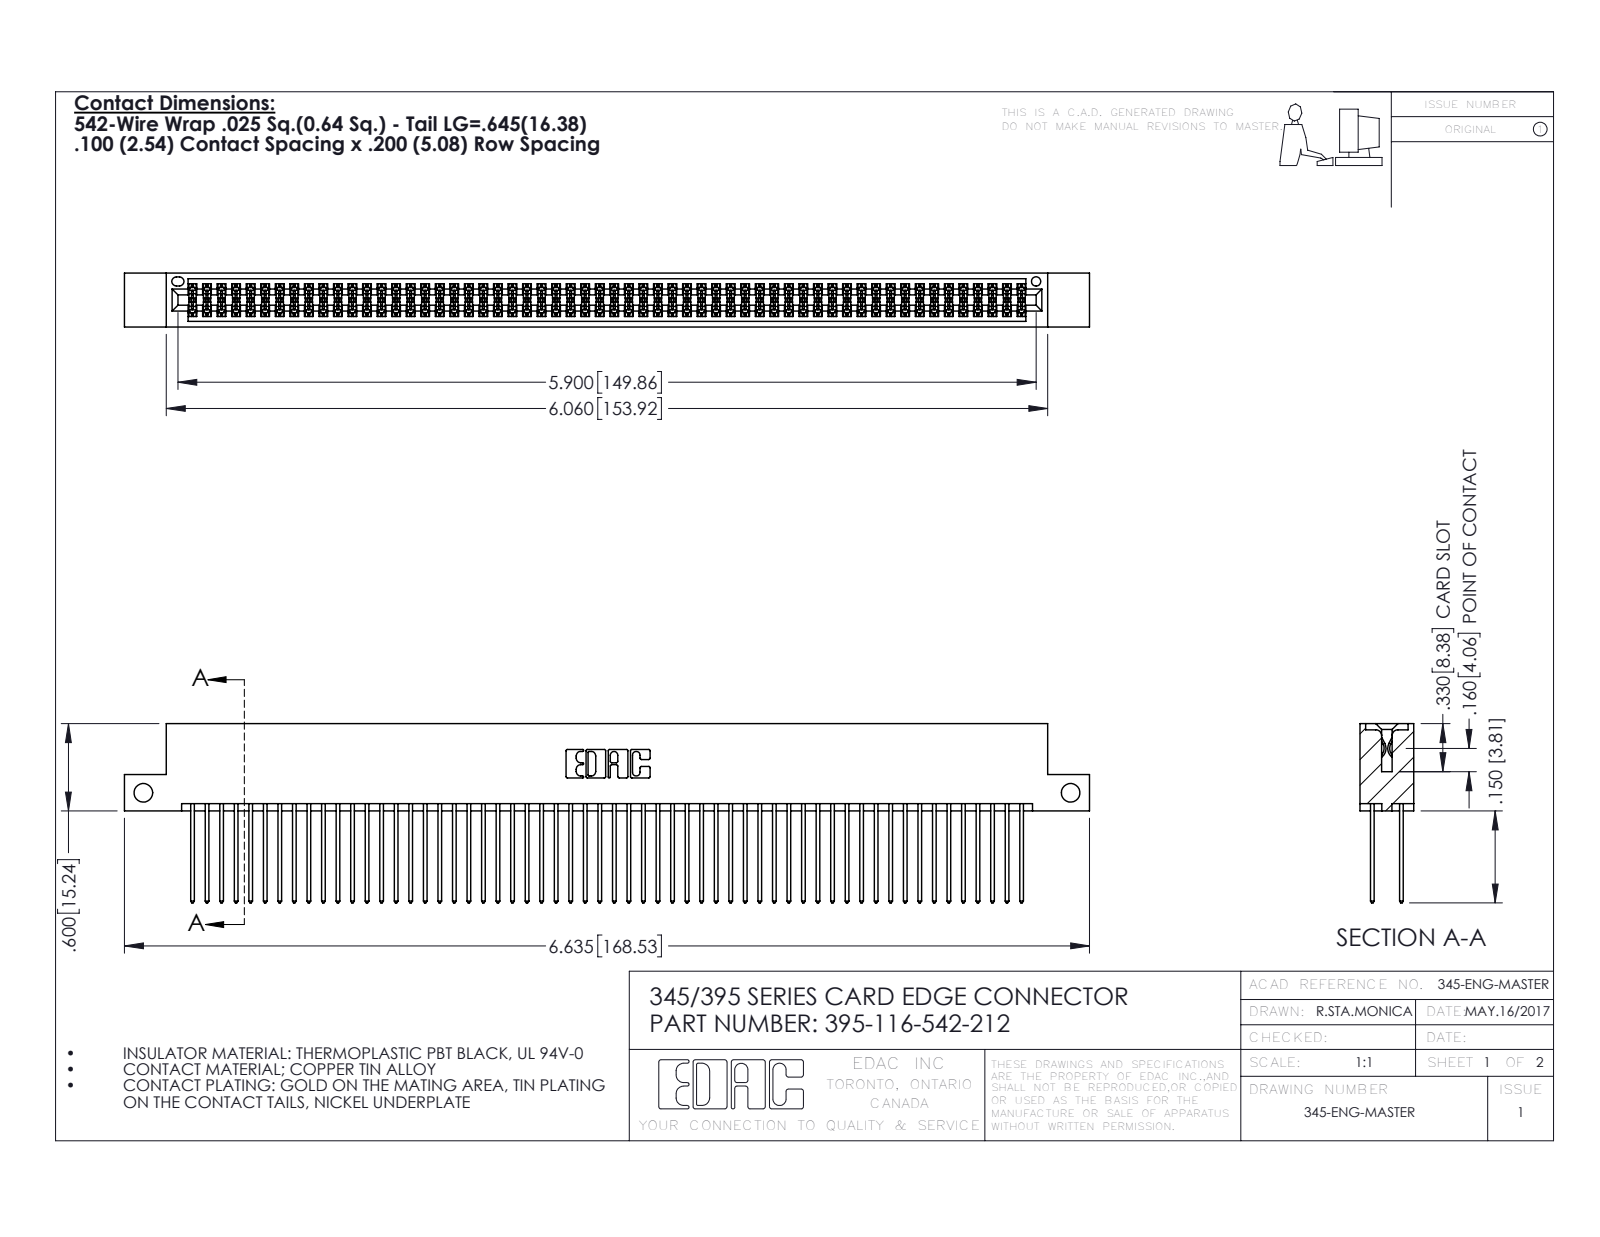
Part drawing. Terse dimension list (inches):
name: 395-116-542-212; 345 Part_Flush Mounting Lugs - Side Mount; 345-292-001_345-293-142
written by: SolidWorks 2016 (CONFIG_CONTROL_DESIGN)
unit: in
bodies: 117 solids, 5926 faces (3908 planar, 2018 cylindrical, 0 other)
size: 6.635 × 1.232 × 0.37
volume: 1.036 in³; area: 43.08 in²
holes: 2× ⌀0.128, 1× ⌀0.064
rounds: 174× R0.006, 116× R0.01, 22× R0.01, 6× R0.007, 6× R0.031, 3× R0.026, 2× R0.014, 2× R0.019
face distances: 0.298, 0.072, 0.2, 0.098, 0.272, 0.025, 0.225, 0.37, 0.175, 0.149
hole spacings: 6.375
